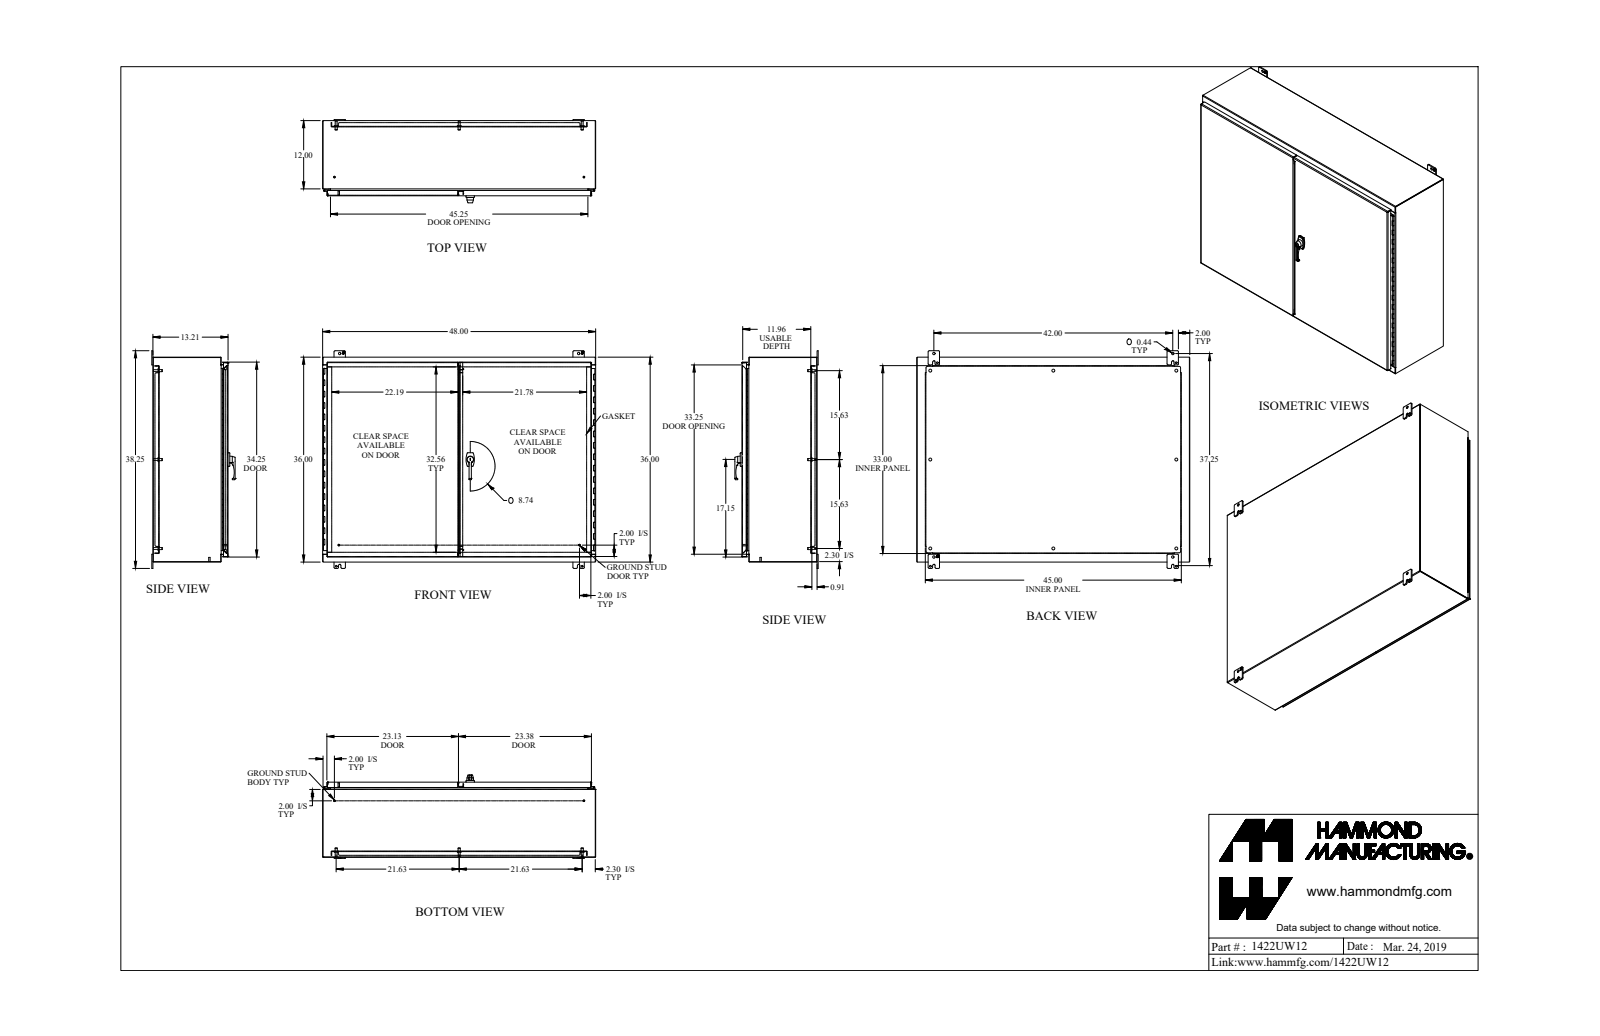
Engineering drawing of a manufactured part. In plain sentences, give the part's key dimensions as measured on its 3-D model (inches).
The part is named "1422UW12". Its 3-D file was written by "SolidWorks 2019 (AUTOMOTIVE_DESIGN)". It is 0 solids with 1727 faces: 1090 planar, 519 cylindrical and 118 other. Overall it measures 48 by 38.25 by 14.637 inches. Round holes: 12 of diameter 0.304, 9 of diameter 0.307, 8 of diameter 0.5, 6 of diameter 0.445, 4 of diameter 0.218, 4 of diameter 0.313, 4 of diameter 0.437, 3 of diameter 0.215, 3 of diameter 0.445, 2 of diameter 0.11, 2 of diameter 0.127, 2 of diameter 0.156. Round bosses or shafts: 10 of diameter 1, 8 of diameter 0.65, 8 of diameter 0.375, 8 of diameter 0.33, 5 of diameter 0.5, 4 of diameter 0.313, 4 of diameter 0.281, 4 of diameter 0.25. Partial cylindrical surfaces (rounded edges, fillets, slot ends): 27 of radius 0.188, 18 of radius 0.048, 18 of radius 0.143, 16 of radius 0.05, 14 of radius 0.036, 14 of radius 0.108, 13 of radius 0.25, 12 of radius 0.116. The main face-to-face distances are 0.072, 0.095, 13.043, 13.115, 0.937, 0.095, 13.138, 13.21, 12.106, 12.011. The hole center spacings are 6, 46.778, 12, 47.919, 18, 46.392, 49.762, 1.735.
